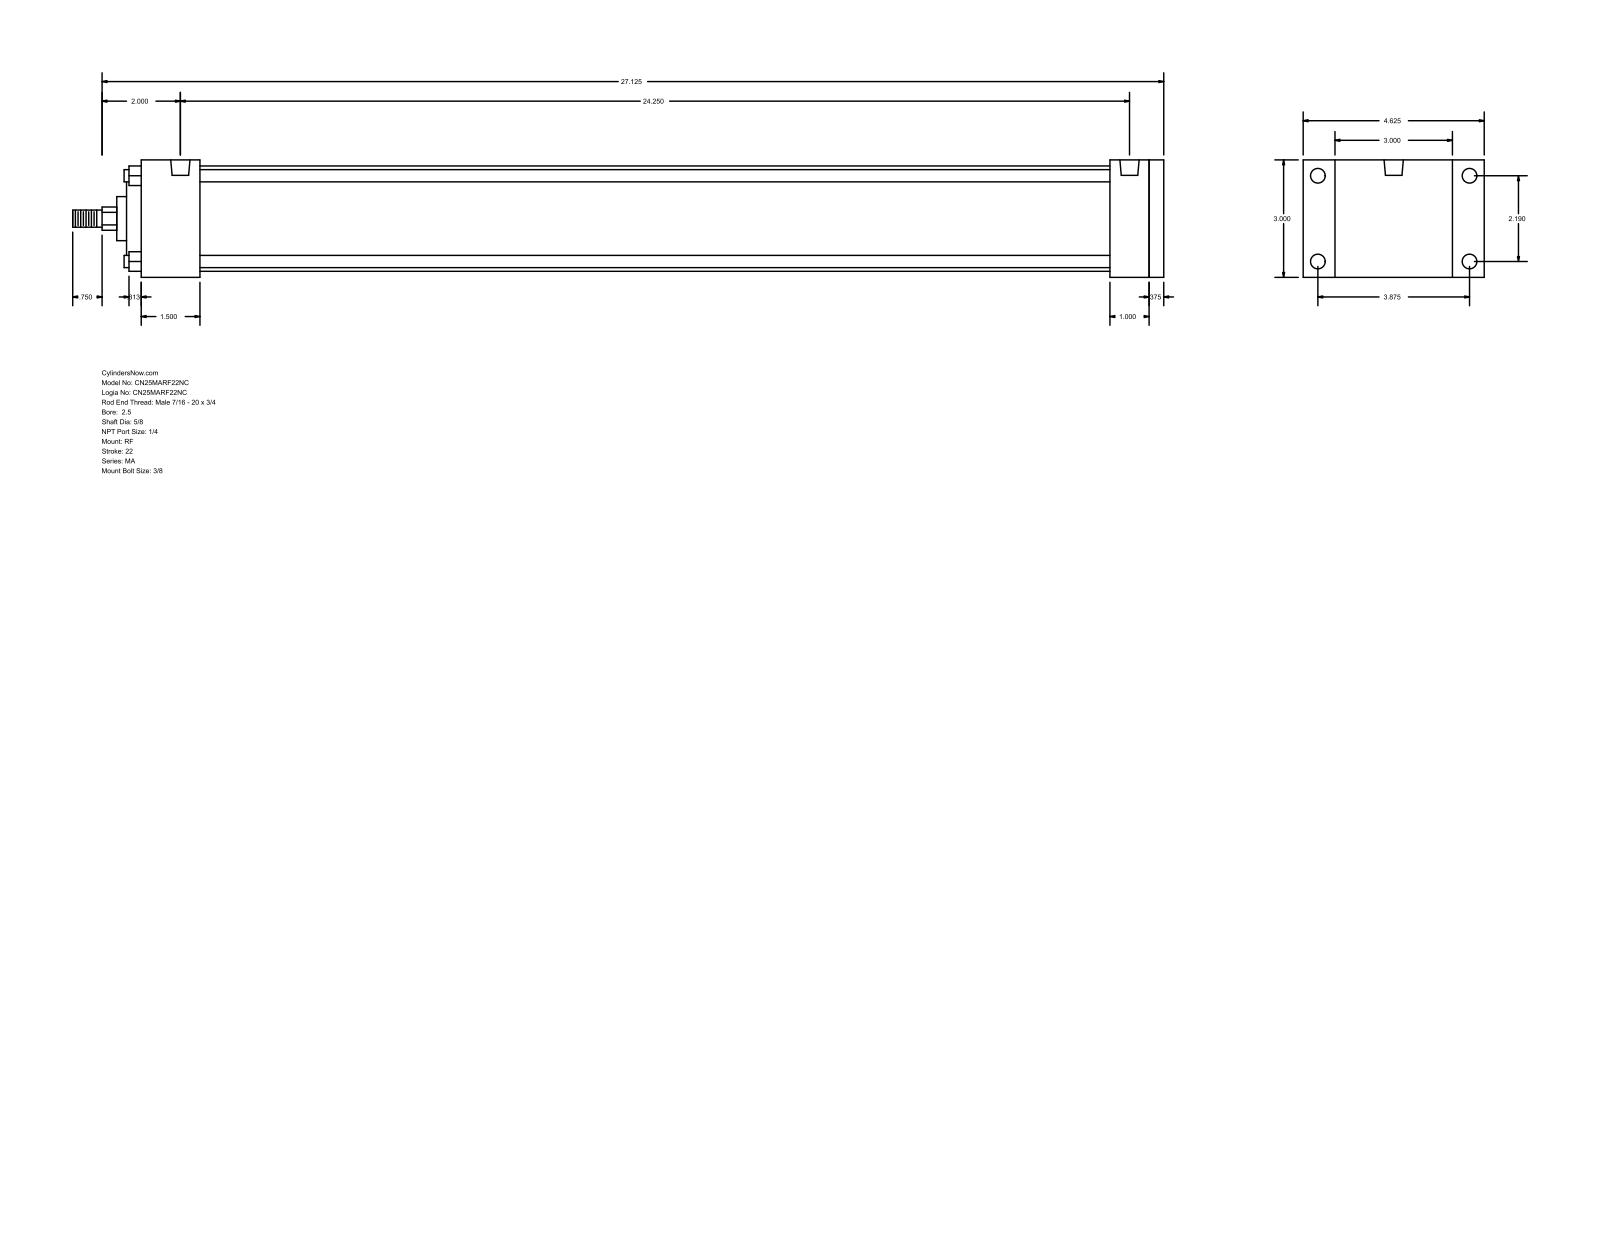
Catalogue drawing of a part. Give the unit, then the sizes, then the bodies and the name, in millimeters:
Units: millimetres
Overall size (bounding box): 708.02 × 117.47 × 76.2
Round holes (diameter × count): ⌀7.94 ×4, ⌀9.53 ×4, ⌀12.49 ×2
Round bosses / shafts (diameter × count): ⌀7.94 ×4, ⌀68.33 ×1, ⌀50.8 ×1, ⌀28.57 ×1, ⌀15.88 ×1, ⌀11.11 ×1
Partial cylindrical surfaces — rounded edges, fillets, slot ends (radius × count): R7.54 ×1
Main face-to-face distances: 76.2, 663.58, 9.53, 654.05, 25.4, 34.93, 38.1, 628.65, 590.55, 615.95
Hole centre spacings: 55.62, 98.42, 113.05, 615.95
Bodies: 0 solids, 94 faces (65 planar, 29 cylindrical, 0 other)
Part name (STEP PRODUCT): MA_RF__0250_0.625
STEP written by: GSSL Pune (CONFIG_CONTROL_DESIGN)
